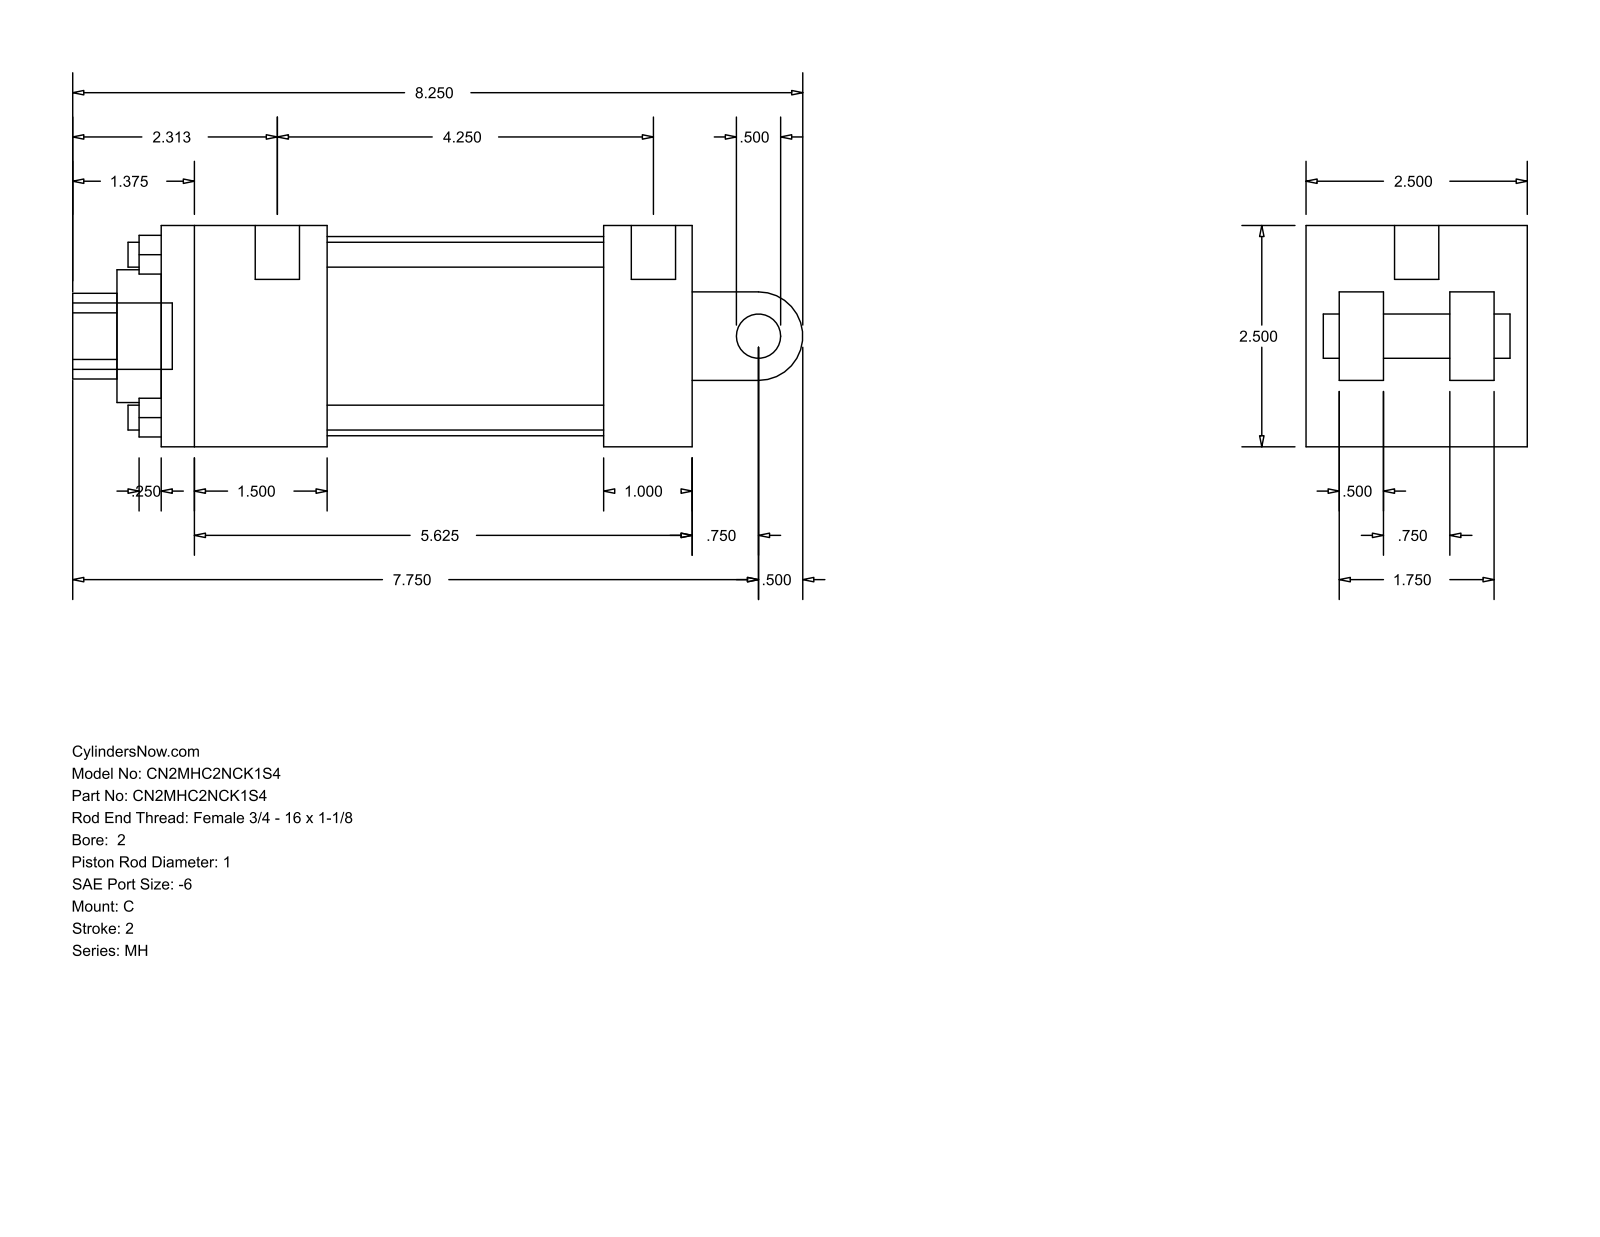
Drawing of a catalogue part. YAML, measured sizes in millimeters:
part_name: "MH_C__0200_1"
step_written_by: "GSSL Pune (CONFIG_CONTROL_DESIGN)"
units: millimeters
bodies: {solids: 0, faces: 99, planar: 70, cylindrical: 29, other: 0}
overall_size: [209.55, 63.5, 63.5]
round_holes:
  - {diameter: 7.14, count: 4}
  - {diameter: 5.56, count: 2}
  - {diameter: 12.7, count: 1}
  - {diameter: 25.4, count: 1}
  - {diameter: 38.1, count: 1}
  - {diameter: 57.15, count: 1}
round_bosses_or_shafts:
  - {diameter: 12.7, count: 2}
  - {diameter: 5.56, count: 2}
  - {diameter: 19.05, count: 1}
partial_cylinders:
  - {radius: 12.29, count: 1}
  - {radius: 12.7, count: 1}
face_to_face_distances: [63.5, 152.4, 12.7, 25.4, 9.52, 47.63, 53.98, 127, 79.37, 104.77]
hole_center_spacings: [33.05, 46.74, 66.1, 3.17]
